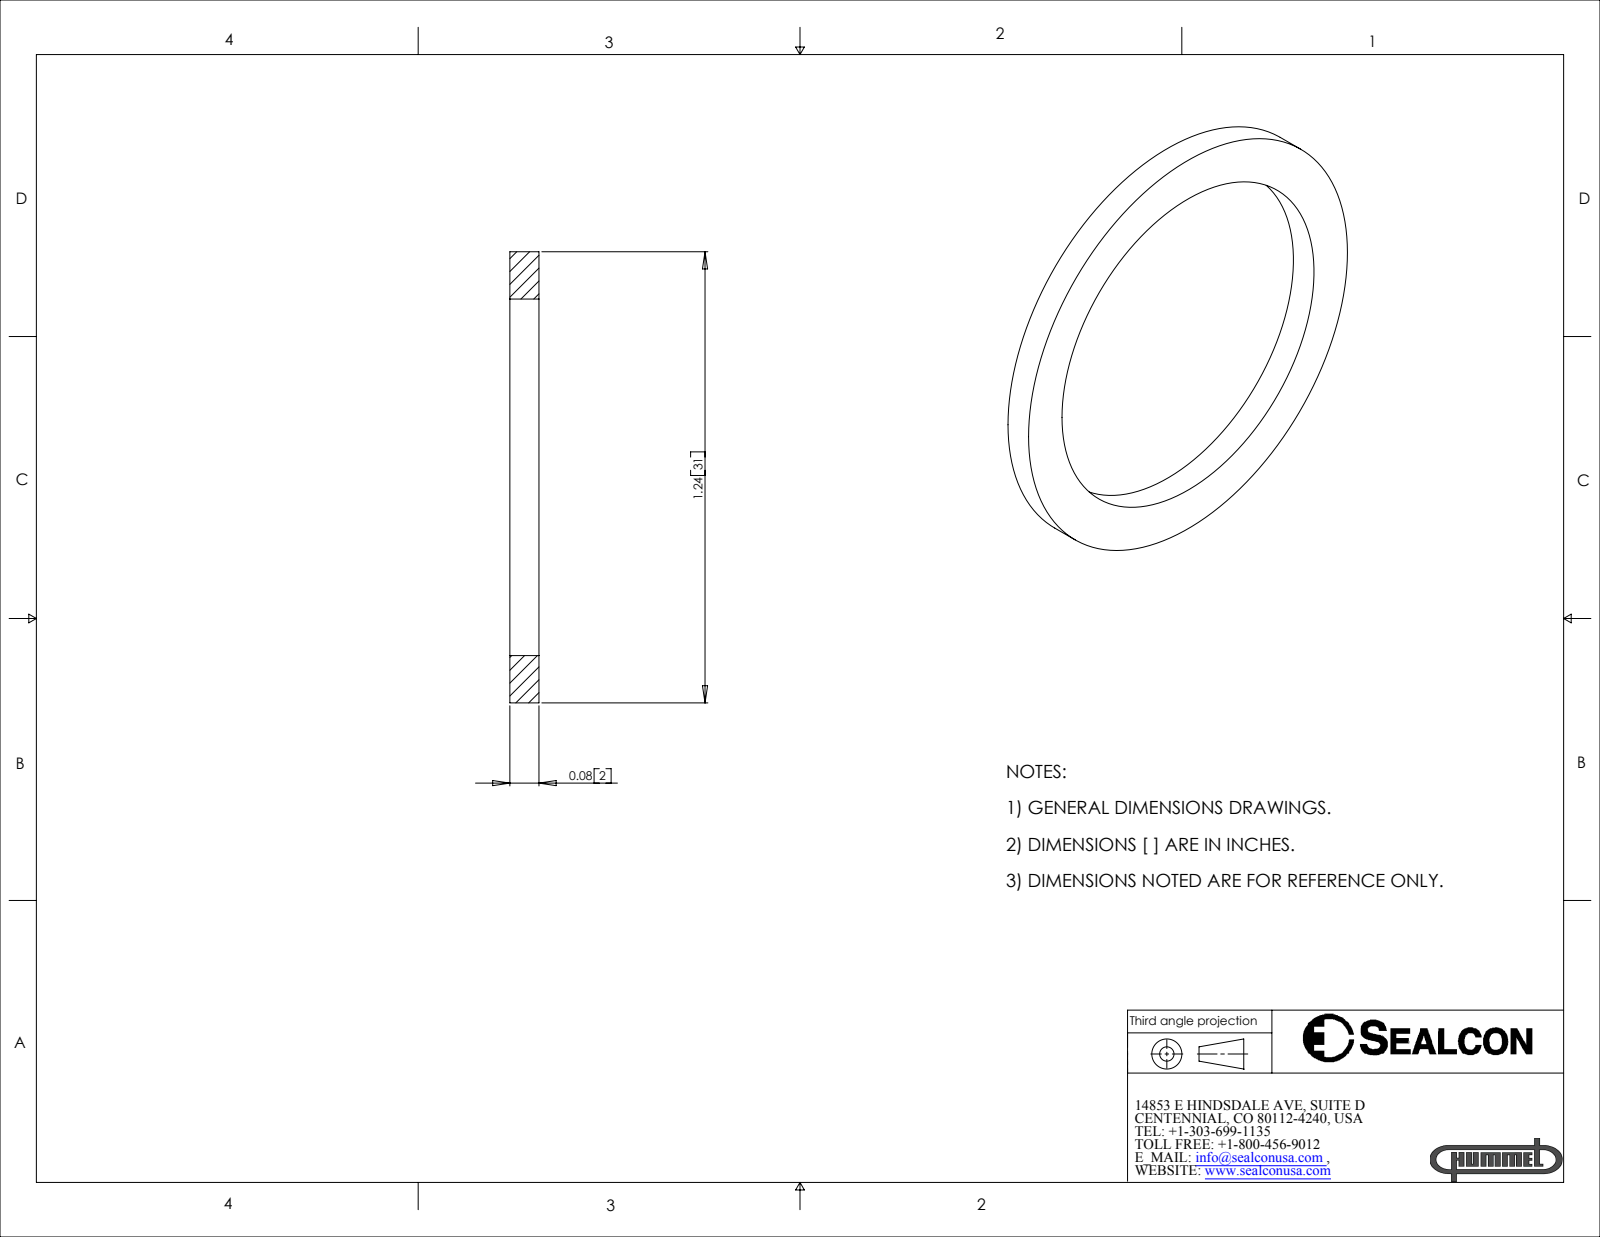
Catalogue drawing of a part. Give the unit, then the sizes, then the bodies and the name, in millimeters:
Units: millimetres
Overall size (bounding box): 31.5 × 31.5 × 2
Round holes (diameter × count): ⌀24.9 ×1
Round bosses / shafts (diameter × count): ⌀31.5 ×1
Main face-to-face distances: 2
Volume: 590 mm³ · Surface area: 945 mm²
Bodies: 1 solid, 6 faces (2 planar, 4 cylindrical, 0 other)
Part name (STEP PRODUCT): SM-25-VT
STEP written by: SolidWorks 2007 (CONFIG_CONTROL_DESIGN)
